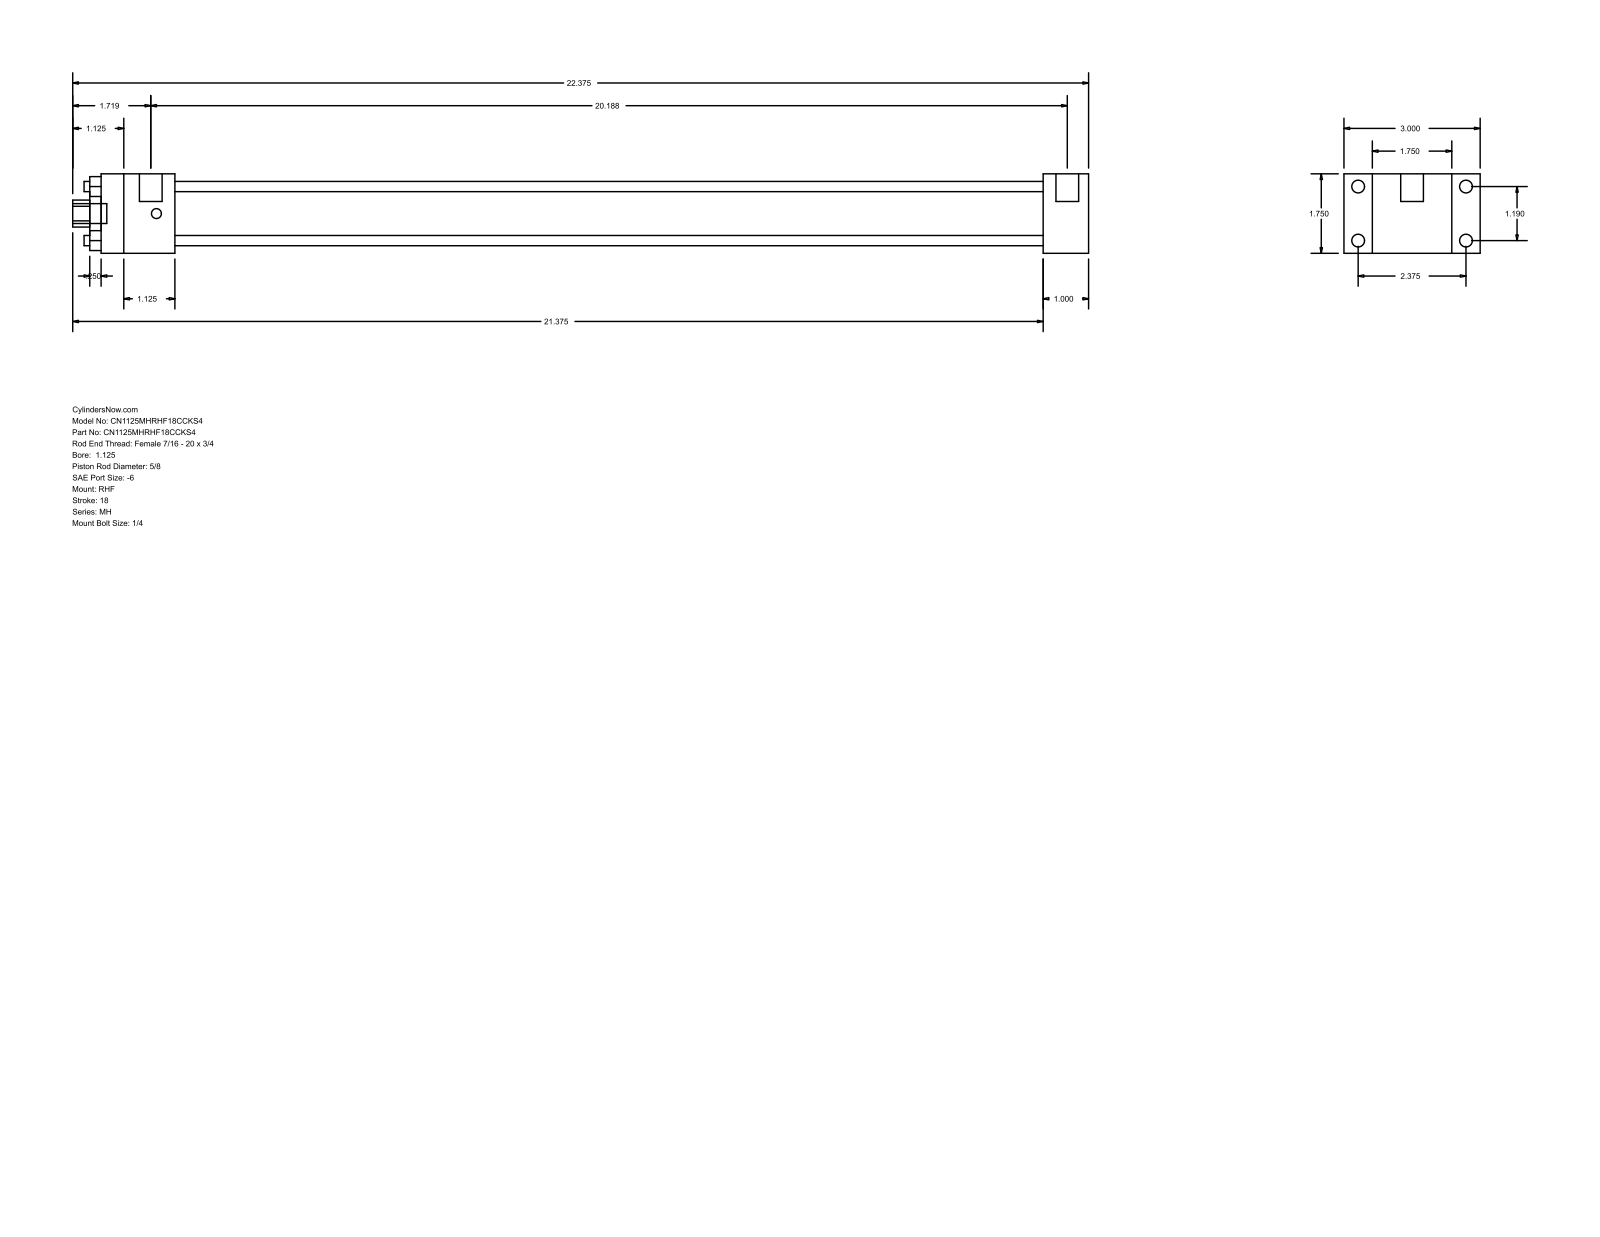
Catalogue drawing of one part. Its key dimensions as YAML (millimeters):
part_name: "MH_RHF__0112_0.625"
step_written_by: "GSSL Pune (CONFIG_CONTROL_DESIGN)"
units: millimeters
bodies: {solids: 0, faces: 88, planar: 60, cylindrical: 28, other: 0}
overall_size: [568.33, 76.2, 44.45]
round_holes:
  - {diameter: 5.71, count: 4}
  - {diameter: 15.88, count: 1}
  - {diameter: 28.57, count: 1}
  - {diameter: 34.92, count: 1}
round_bosses_or_shafts:
  - {diameter: 7.14, count: 4}
  - {diameter: 5.56, count: 4}
  - {diameter: 12.7, count: 2}
  - {diameter: 11.11, count: 1}
partial_cylinders:
  - {radius: 7.54, count: 1}
face_to_face_distances: [44.46, 15.87, 60.33, 25.41, 76.2, 485.77, 511.18, 41.27, 527.04, 552.45]
hole_center_spacings: [21.37, 30.22, 42.74]
